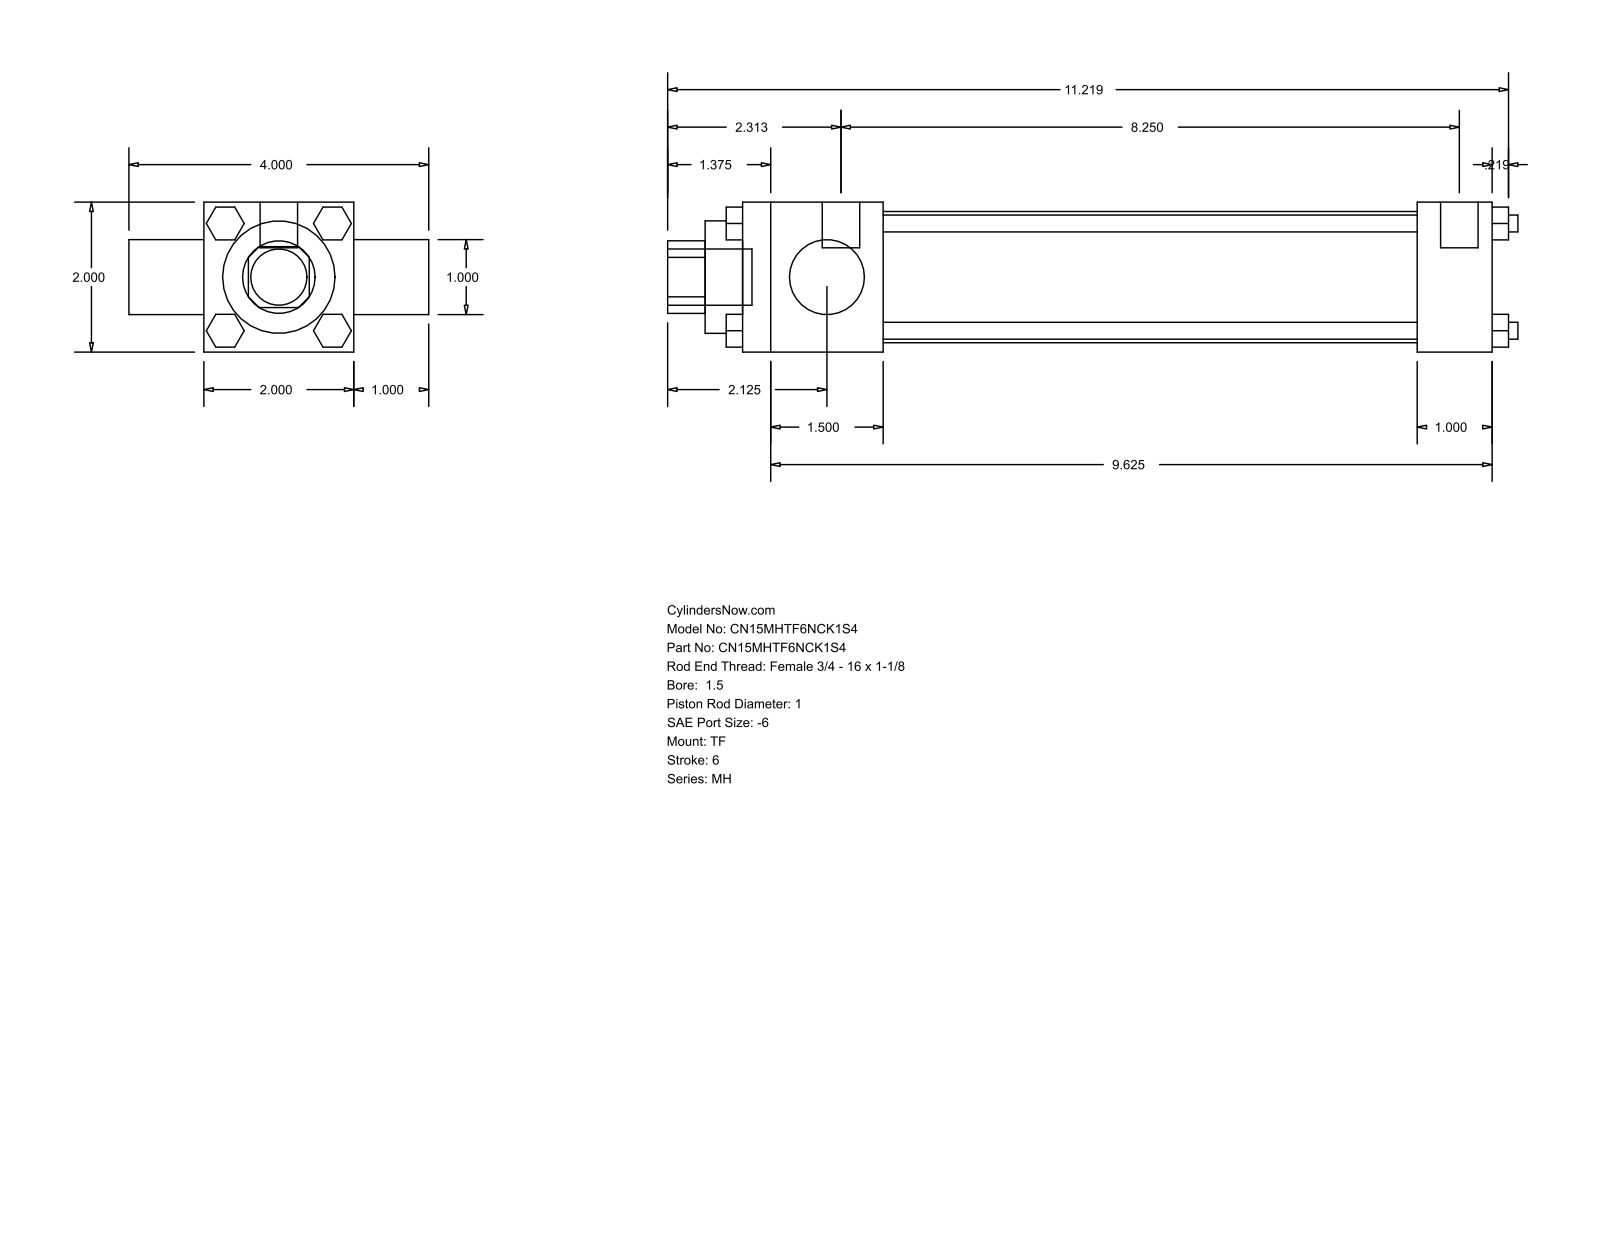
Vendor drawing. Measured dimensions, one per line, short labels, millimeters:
name: MH_TF__0150_1
written by: GSSL Pune (CONFIG_CONTROL_DESIGN)
unit: mm
bodies: 0 solids, 120 faces (92 planar, 28 cylindrical, 0 other)
size: 288.13 × 101.6 × 50.8
holes: 2× ⌀25.4, 1× ⌀38.1, 1× ⌀44.45
bosses: 4× ⌀5.71, 3× ⌀5.56, 2× ⌀12.7, 1× ⌀19.05
rounds: 1× R12.29
face distances: 50.8, 25.4, 254, 76.2, 47.63, 206.37, 228.6, 180.97, 259.56, 12.7
